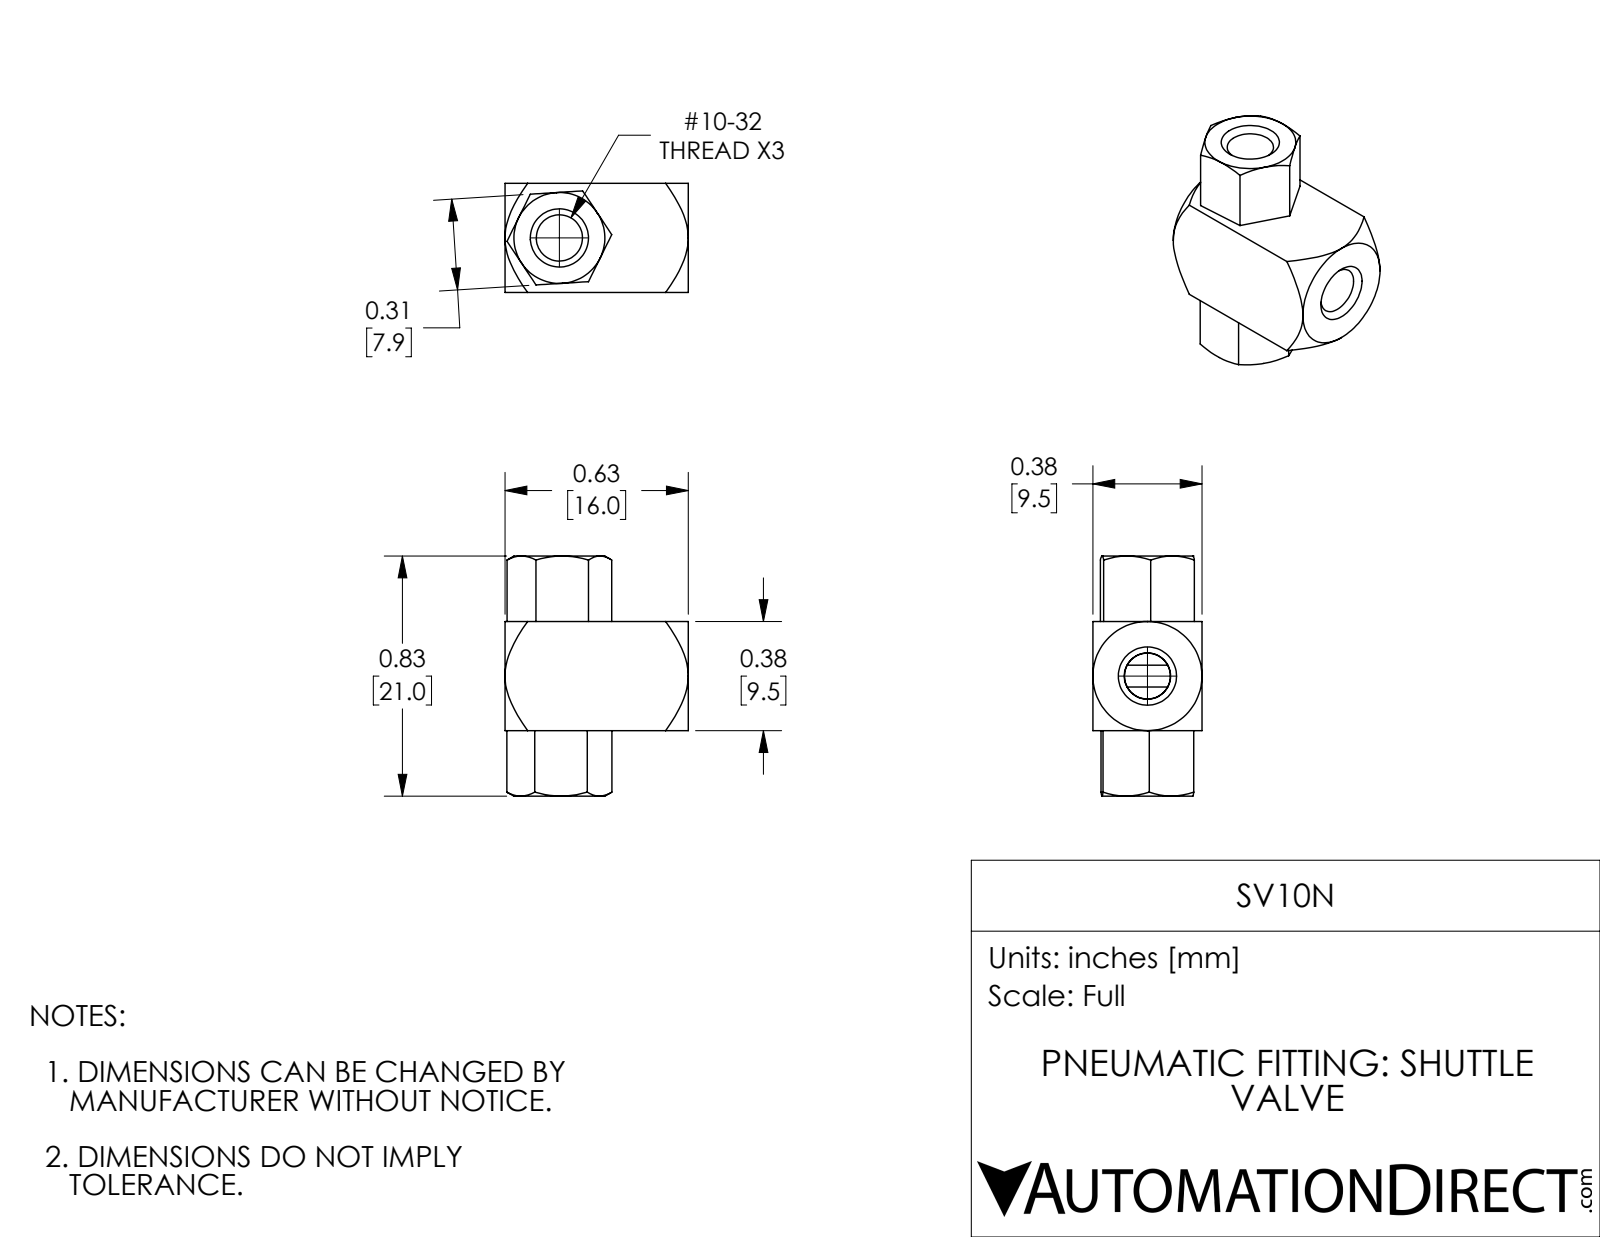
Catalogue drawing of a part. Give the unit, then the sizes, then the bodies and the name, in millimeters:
Units: millimetres
Overall size (bounding box): 21 × 16 × 9.5
Round holes (diameter × count): ⌀4 ×2, ⌀4 ×1
Round bosses / shafts (diameter × count): ⌀6.4 ×1
Main face-to-face distances: 9.5, 8, 5.7, 15.2, 16, 9.5, 11.4, 3.8, 5.7, 21
Volume: 1 640 mm³ · Surface area: 1 820 mm²
Bodies: 3 solids, 68 faces (24 planar, 14 cylindrical, 30 other)
Part name (STEP PRODUCT): SV10N
STEP written by: SolidWorks 2018 (AUTOMOTIVE_DESIGN)
